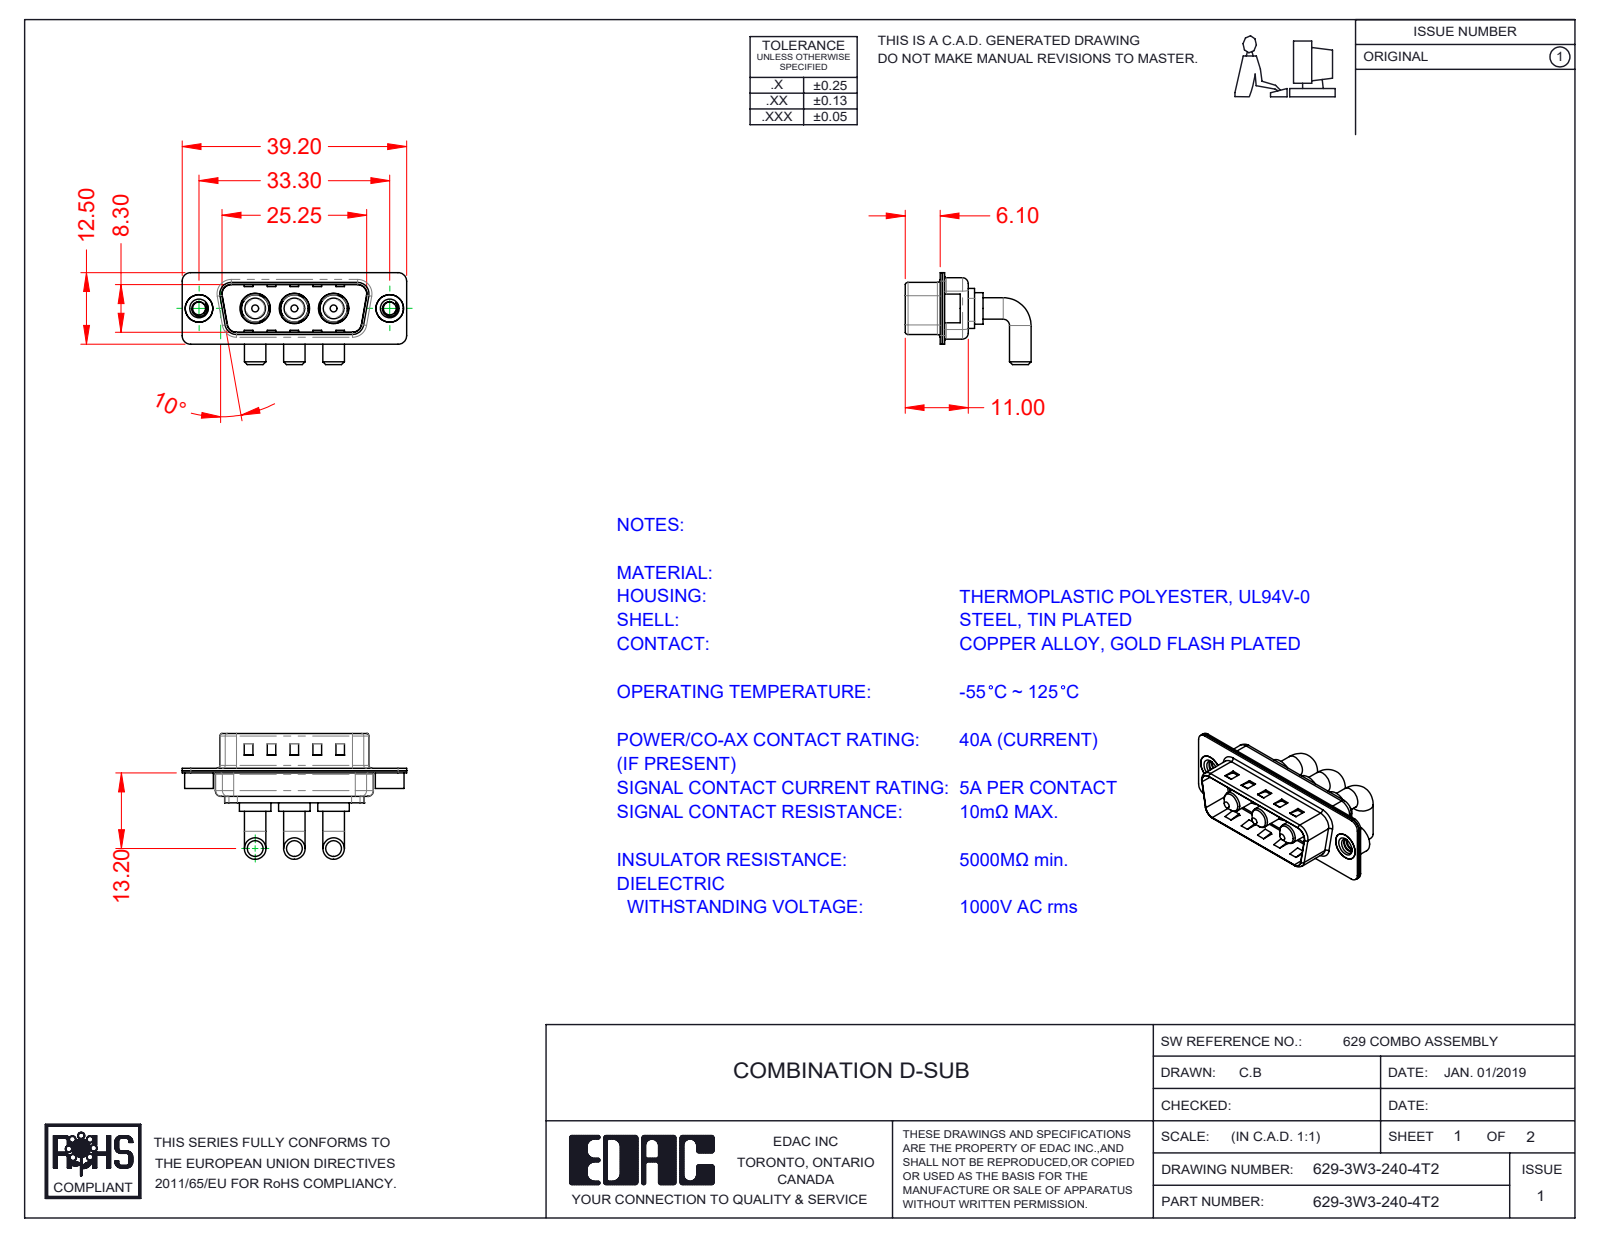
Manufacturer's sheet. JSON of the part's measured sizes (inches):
{"part_name": "629Combo Shell Rear_15 Contacts; Power Pin_40A RA; 629Combo Threaded Rivet_2; 629Combo Housing_3W3 (+2 more)", "step_written_by": "SolidWorks 2020 (CONFIG_CONTROL_DESIGN)", "units": "inches", "bodies": {"solids": 11, "faces": 469, "planar": 169, "cylindrical": 196, "other": 104}, "overall_size": [1.543, 0.865, 0.632], "volume_in3": 0.151, "surface_area_in2": 7.938, "round_holes": [[0.191, 3], [0.209, 3], [0.089, 2], [0.157, 2], [0.189, 2]], "round_bosses_or_shafts": [[0.148, 6], [0.217, 3], [0.205, 3], [0.187, 3], [0.142, 3], [0.197, 2], [0.193, 2]], "partial_cylinders_radius": [[0.059, 16], [0.079, 12], [0.02, 8], [0.063, 8], [0.01, 4], [0.024, 4], [0.026, 4], [0.035, 4]], "face_to_face_distances": [0.016, 0.031, 0.374, 0.358, 0.343, 0.39, 0.03, 0.047, 0.014, 0.236], "hole_center_spacings": [0.27, 0.386, 0.656, 0.925, 0.539, 1.311]}
